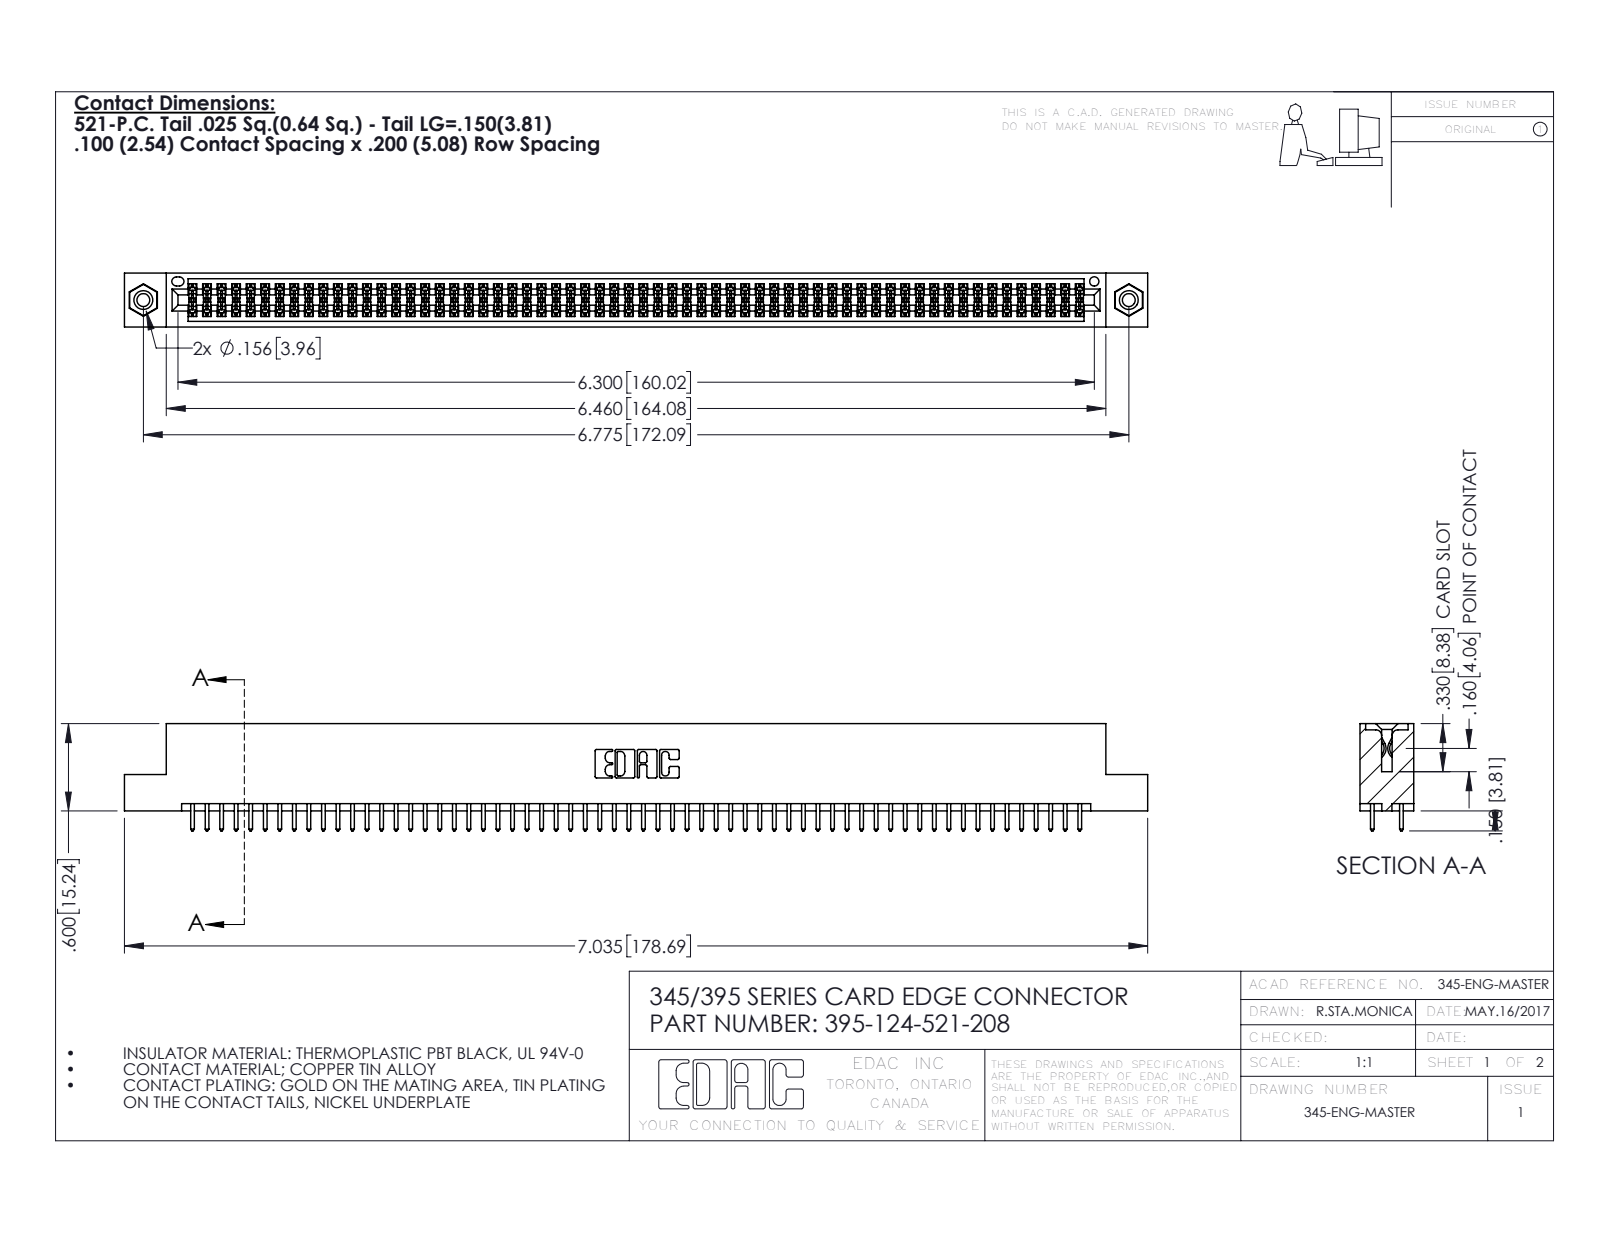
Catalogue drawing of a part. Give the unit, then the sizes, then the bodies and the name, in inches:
Units: inches
Overall size (bounding box): 7.035 × 0.737 × 0.37
Round holes (diameter × count): ⌀0.089 ×2, ⌀0.125 ×2, ⌀0.156 ×2, ⌀0.064 ×1
Round bosses / shafts (diameter × count): ⌀0.155 ×2
Partial cylindrical surfaces — rounded edges, fillets, slot ends (radius × count): R0.006 ×186, R0.01 ×124, R0.01 ×22, R0.007 ×6, R0.031 ×6, R0.026 ×3, R0.014 ×2, R0.019 ×2
Main face-to-face distances: 0.072, 0.298, 0.2, 0.098, 0.272, 0.025, 0.37, 0.225, 0.175, 0.149
Hole centre spacings: 0.27, 6.539, 6.775
Volume: 1.067 in³ · Surface area: 40.18 in²
Bodies: 127 solids, 6386 faces (4204 planar, 2166 cylindrical, 16 other)
Part name (STEP PRODUCT): 395-124-521-208; 345 Part_Flush Mounting Lugs - 0.156 Dia-TI; 345-292-001_345-293-121; 345-250-001_345-250-003-102
STEP written by: SolidWorks 2016 (CONFIG_CONTROL_DESIGN)
